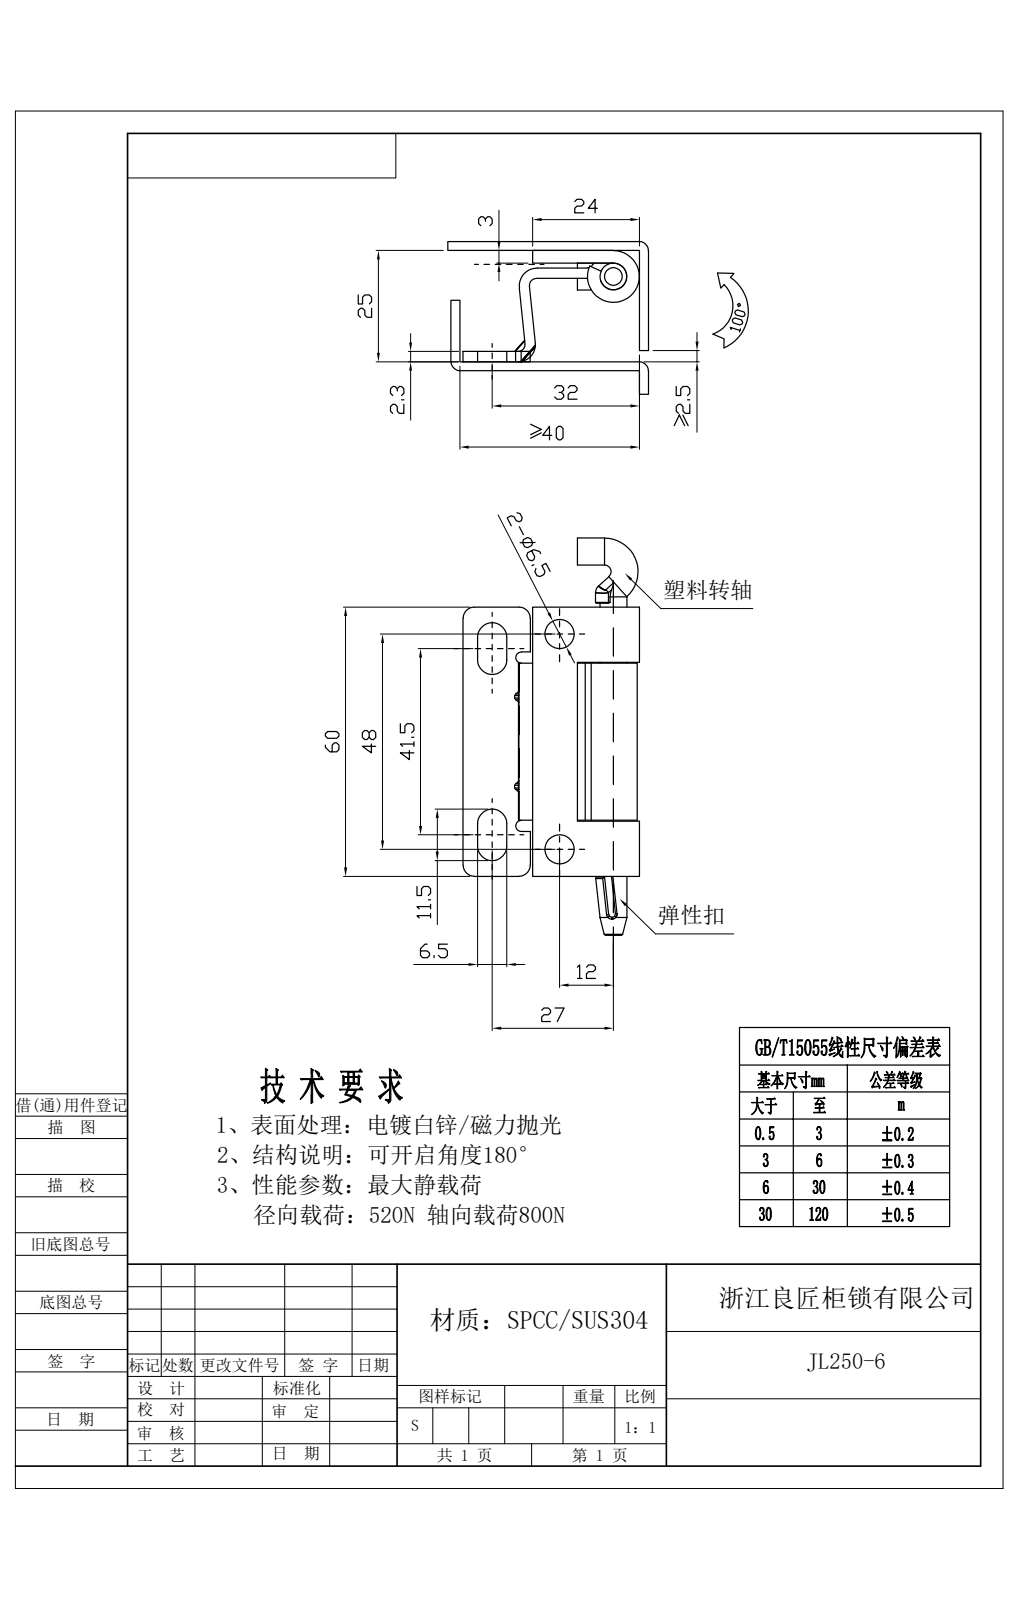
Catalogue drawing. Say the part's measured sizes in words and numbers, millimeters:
Its 3-D file was written by "Rhino 8.5 (CONFIG_CONTROL_DESIGN)". It is 2 solids with 113 faces: 55 planar, 44 cylindrical and 14 other. Overall it measures 90.17 by 41.5 by 25 millimeters. Its volume is 10 018 cubic millimeters and its surface area 11 163 square millimeters. Round holes: 2 of diameter 6.5. Round bosses or shafts: 3 of diameter 6, 1 of diameter 11.6, 1 of diameter 10.6, 1 of diameter 5. Partial cylindrical surfaces (rounded edges, fillets, slot ends): 6 of radius 2.5, 4 of radius 3.25, 3 of radius 1.5, 2 of radius 1.25, 2 of radius 1.6, 1 of radius 0.15, 1 of radius 0.75, 1 of radius 2.8. The main face-to-face distances are 3, 2.3, 22, 25, 19.7, 22.7, 2.31, 18.61, 16.31, 3.39. The hole center spacings are 48.
